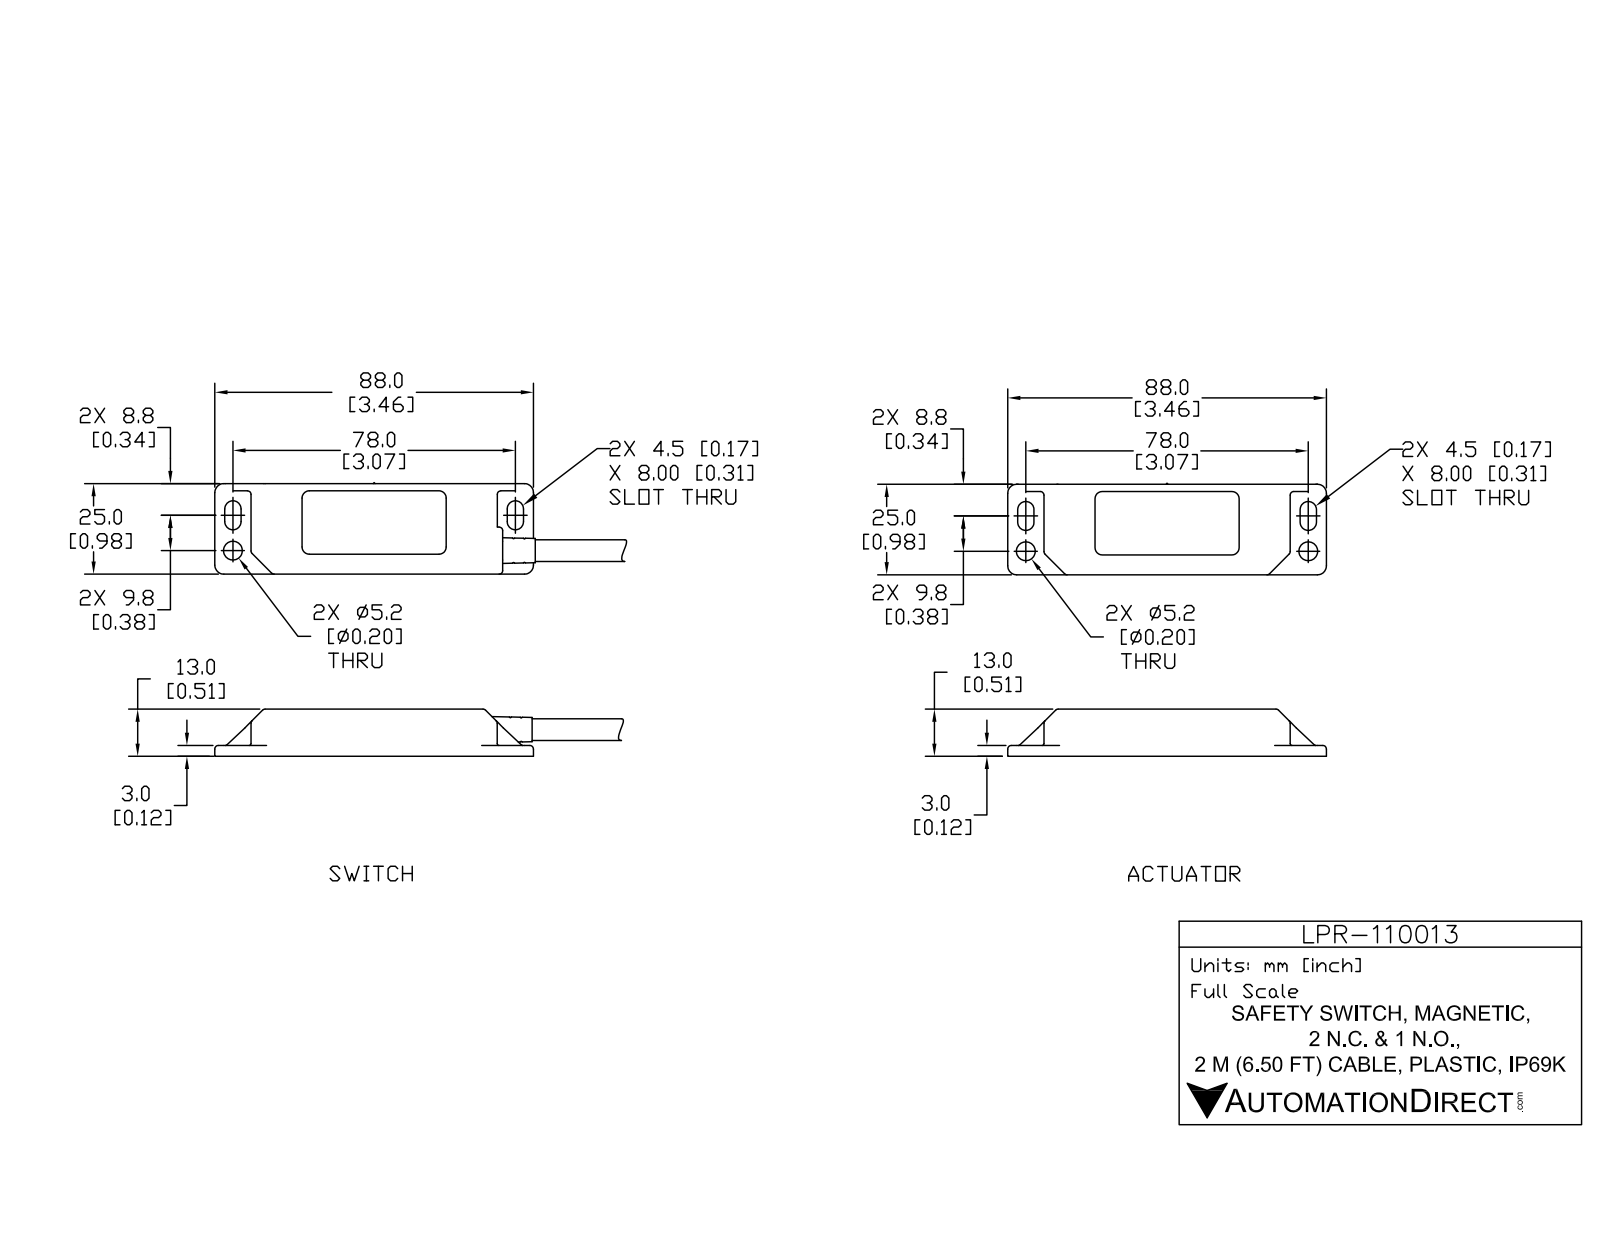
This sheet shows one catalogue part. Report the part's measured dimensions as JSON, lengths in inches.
{"part_name": "LPR-110013_1; LPR-110013_2; LPR-110013", "step_written_by": "SolidWorks 2017 (AUTOMOTIVE_DESIGN)", "units": "inches", "bodies": {"solids": 11, "faces": 1058, "planar": 401, "cylindrical": 303, "other": 354}, "overall_size": [8.849, 1.992, 0.543], "volume_in3": 1.638, "surface_area_in2": 46.88, "round_holes": [[0.197, 4], [0.205, 4], [0.119, 1], [0.173, 1], [0.213, 1], [0.232, 1], [0.276, 1]], "round_bosses_or_shafts": [[0.079, 4], [0.193, 2], [0.091, 2], [0.339, 1], [0.299, 1], [0.28, 1], [0.236, 1], [0.209, 1]], "partial_cylinders_radius": [[0.02, 116], [0.039, 49], [0.079, 10], [0.089, 8], [0.098, 8], [0.012, 6], [0.189, 1]], "face_to_face_distances": [0.067, 0.441, 0.079, 0.374, 0.059, 0.071, 0.508, 0.445, 0.512, 0.988], "hole_center_spacings": [0.748, 1.097, 1.19, 1.275, 1.48, 1.571, 1.784, 1.895]}
